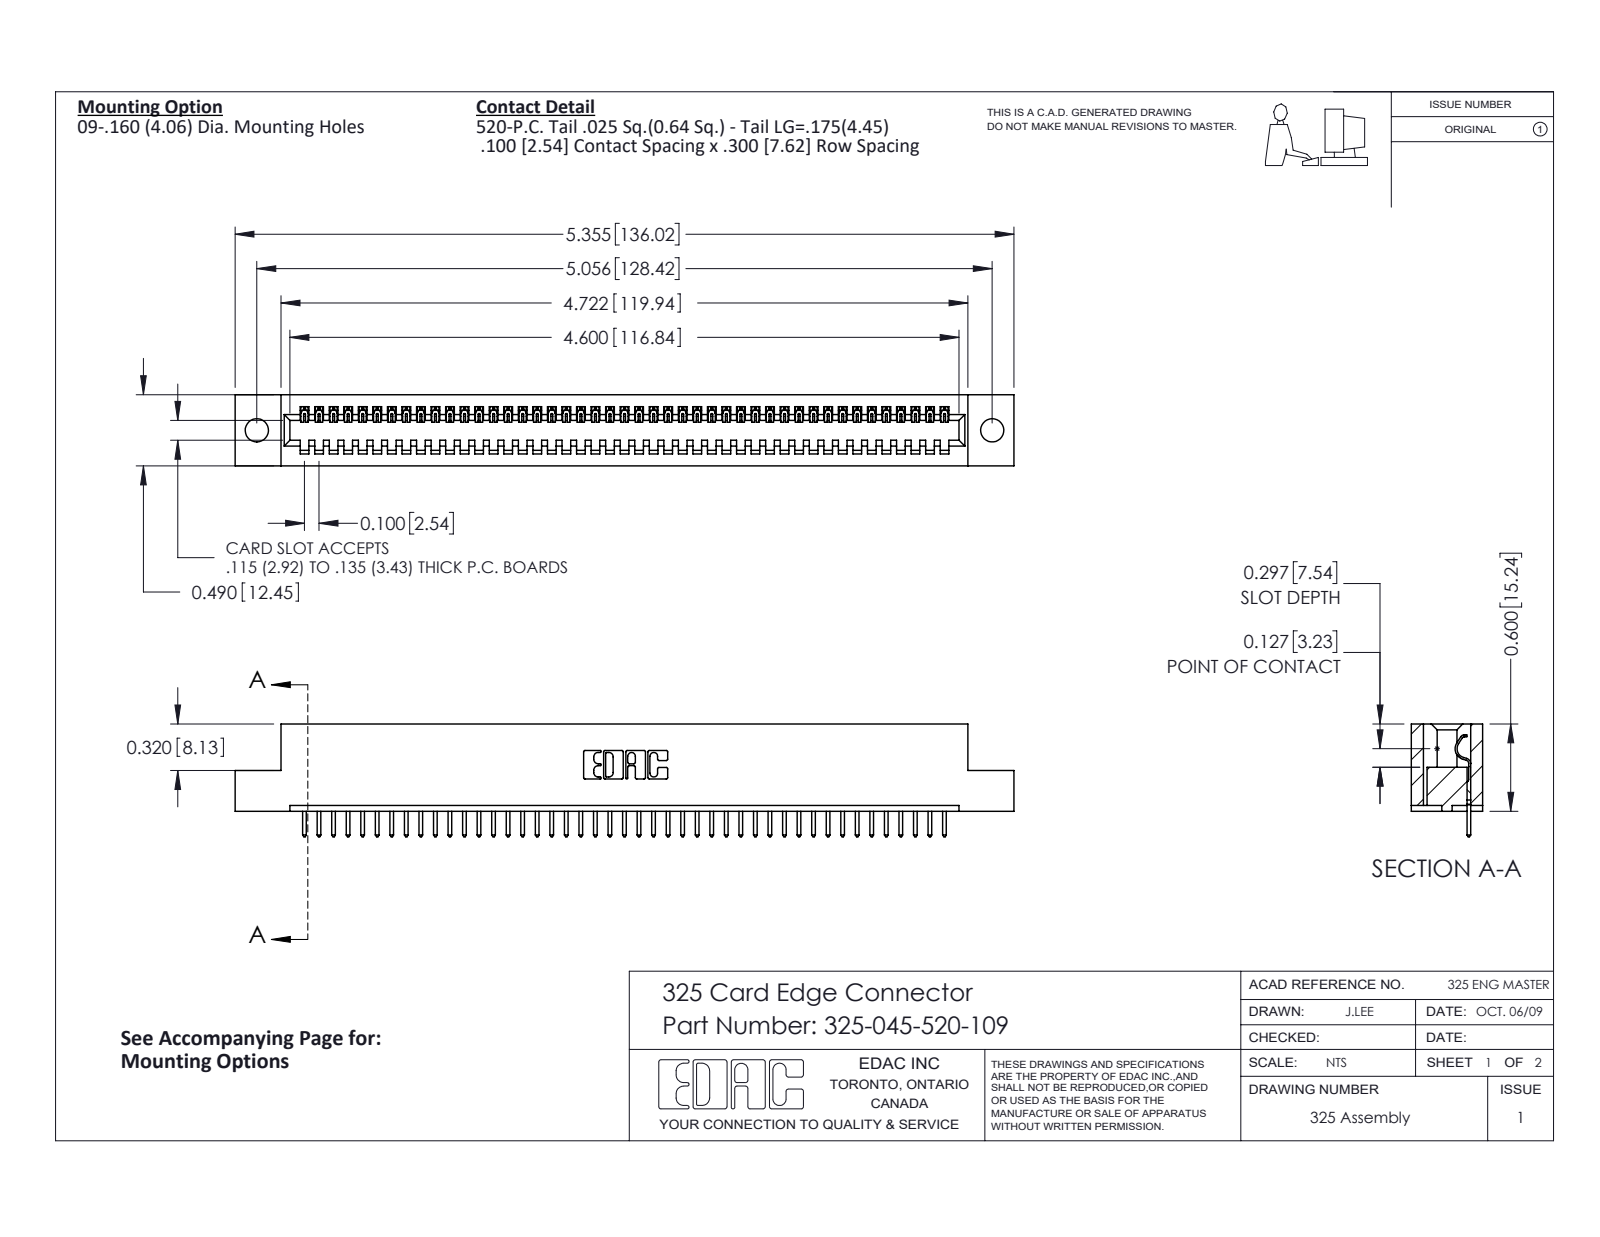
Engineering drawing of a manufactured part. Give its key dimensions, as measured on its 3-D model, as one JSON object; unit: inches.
{"part_name": "325 Part_.160 TH; 325-292-001_325-293-120; 325-045-520-109", "step_written_by": "SolidWorks 2016 (CONFIG_CONTROL_DESIGN)", "units": "inches", "bodies": {"solids": 46, "faces": 2724, "planar": 1960, "cylindrical": 764, "other": 0}, "overall_size": [5.355, 0.775, 0.49], "volume_in3": 1.034, "surface_area_in2": 27.88, "round_holes": [[0.16, 2]], "partial_cylinders_radius": [[0.006, 90], [0.01, 90], [0.01, 22], [0.007, 6], [0.031, 6], [0.026, 3], [0.014, 1], [0.022, 1]], "face_to_face_distances": [0.083, 0.407, 0.49, 0.3, 0.107, 0.383, 0.025, 0.325, 0.56, 0.263], "hole_center_spacings": [5.056]}
